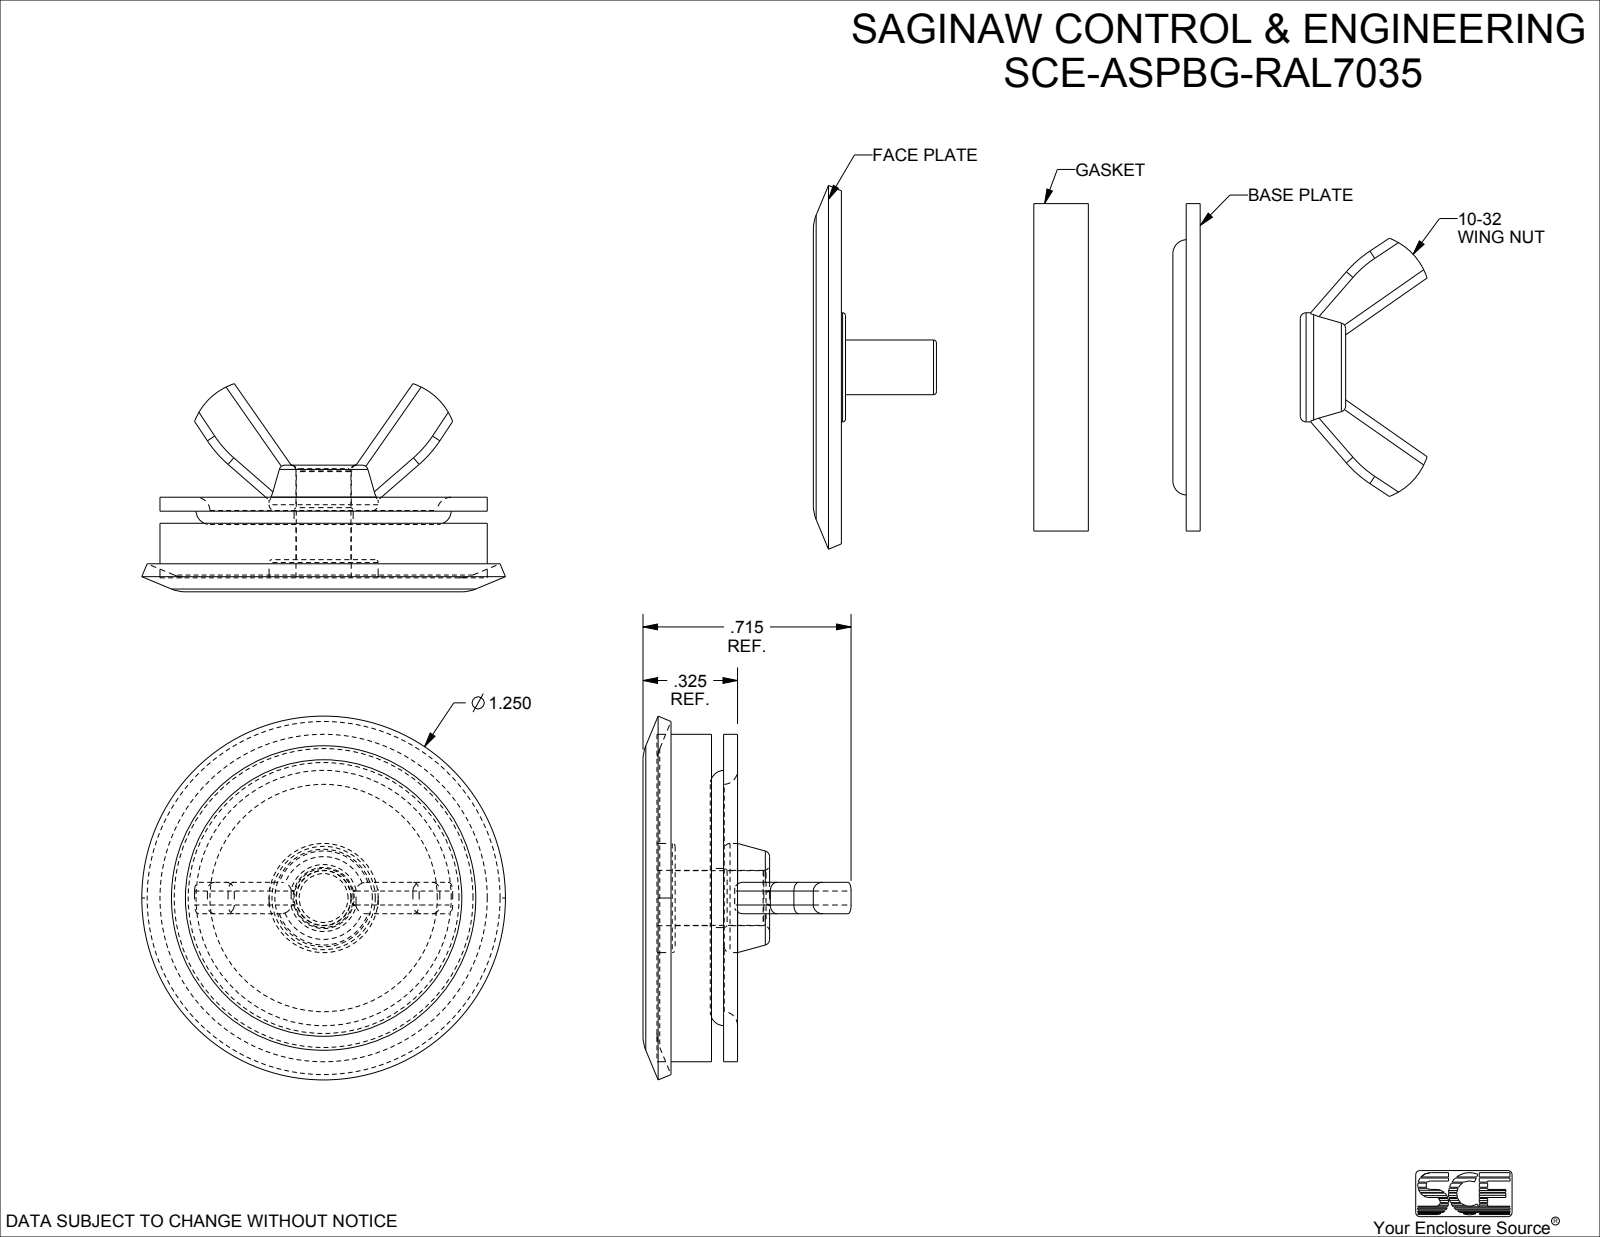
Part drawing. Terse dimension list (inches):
name: SCE-ASPBG-RAL7035
written by: SolidWorks 2019 (CONFIG_CONTROL_DESIGN)
unit: in
bodies: 5 solids, 79 faces (28 planar, 24 cylindrical, 27 other)
size: 1.25 × 1.25 × 0.754
volume: 0.328 in³; area: 8.823 in²
holes: 1× ⌀0.19, 1× ⌀0.203
bosses: 1× ⌀1.125, 1× ⌀0.375, 1× ⌀0.188
rounds: 12× R0.03, 2× R0.22, 2× R0.4
face distances: 0.048, 0.187, 0.27, 0.046, 0.315, 0.235, 0.082, 0.318, 0.034, 0.222
